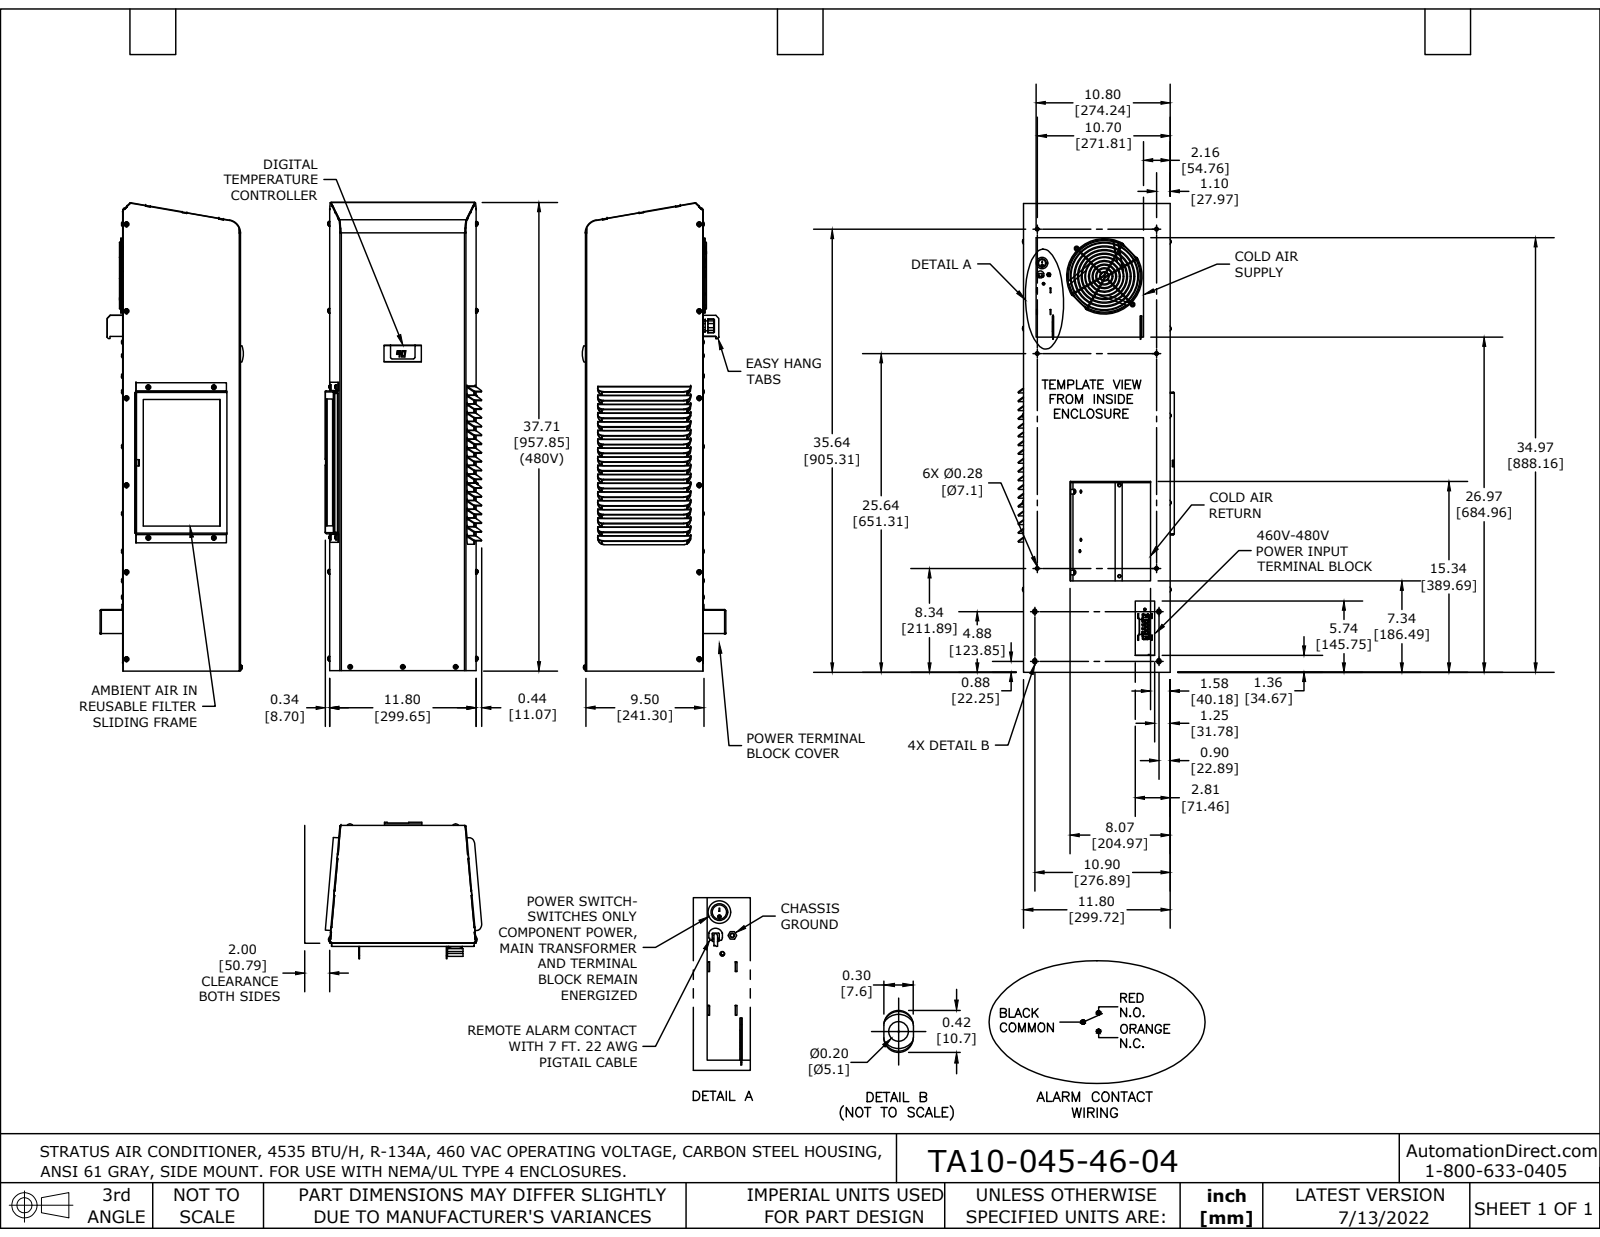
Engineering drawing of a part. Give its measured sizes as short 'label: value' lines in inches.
name: TA10-045-46-04
written by: SolidWorks 2021 (AUTOMOTIVE_DESIGN)
unit: in
bodies: 1 solid, 1744 faces (1077 planar, 497 cylindrical, 170 other)
size: 32.024 × 12.576 × 11.549
volume: 136.5 in³; area: 3 197 in²
holes: 11× ⌀0.159, 5× ⌀0.204, 1× ⌀6
bosses: 7× ⌀0.19, 2× ⌀0.379, 2× ⌀0.353, 2× ⌀0.248, 1× ⌀6.07, 1× ⌀0.906, 1× ⌀0.087
rounds: 45× R0.015, 42× R0.01, 36× R0.5, 36× R0.506, 28× R0.1, 21× R0.058, 21× R0.116, 13× R0.03
face distances: 0.058, 9.435, 9.377, 0.058, 9.493, 0.09, 0.25, 0.308, 9.685, 9.743
hole spacings: 7, 14, 21, 1.732, 5.3, 6.565, 10.869, 12.12
